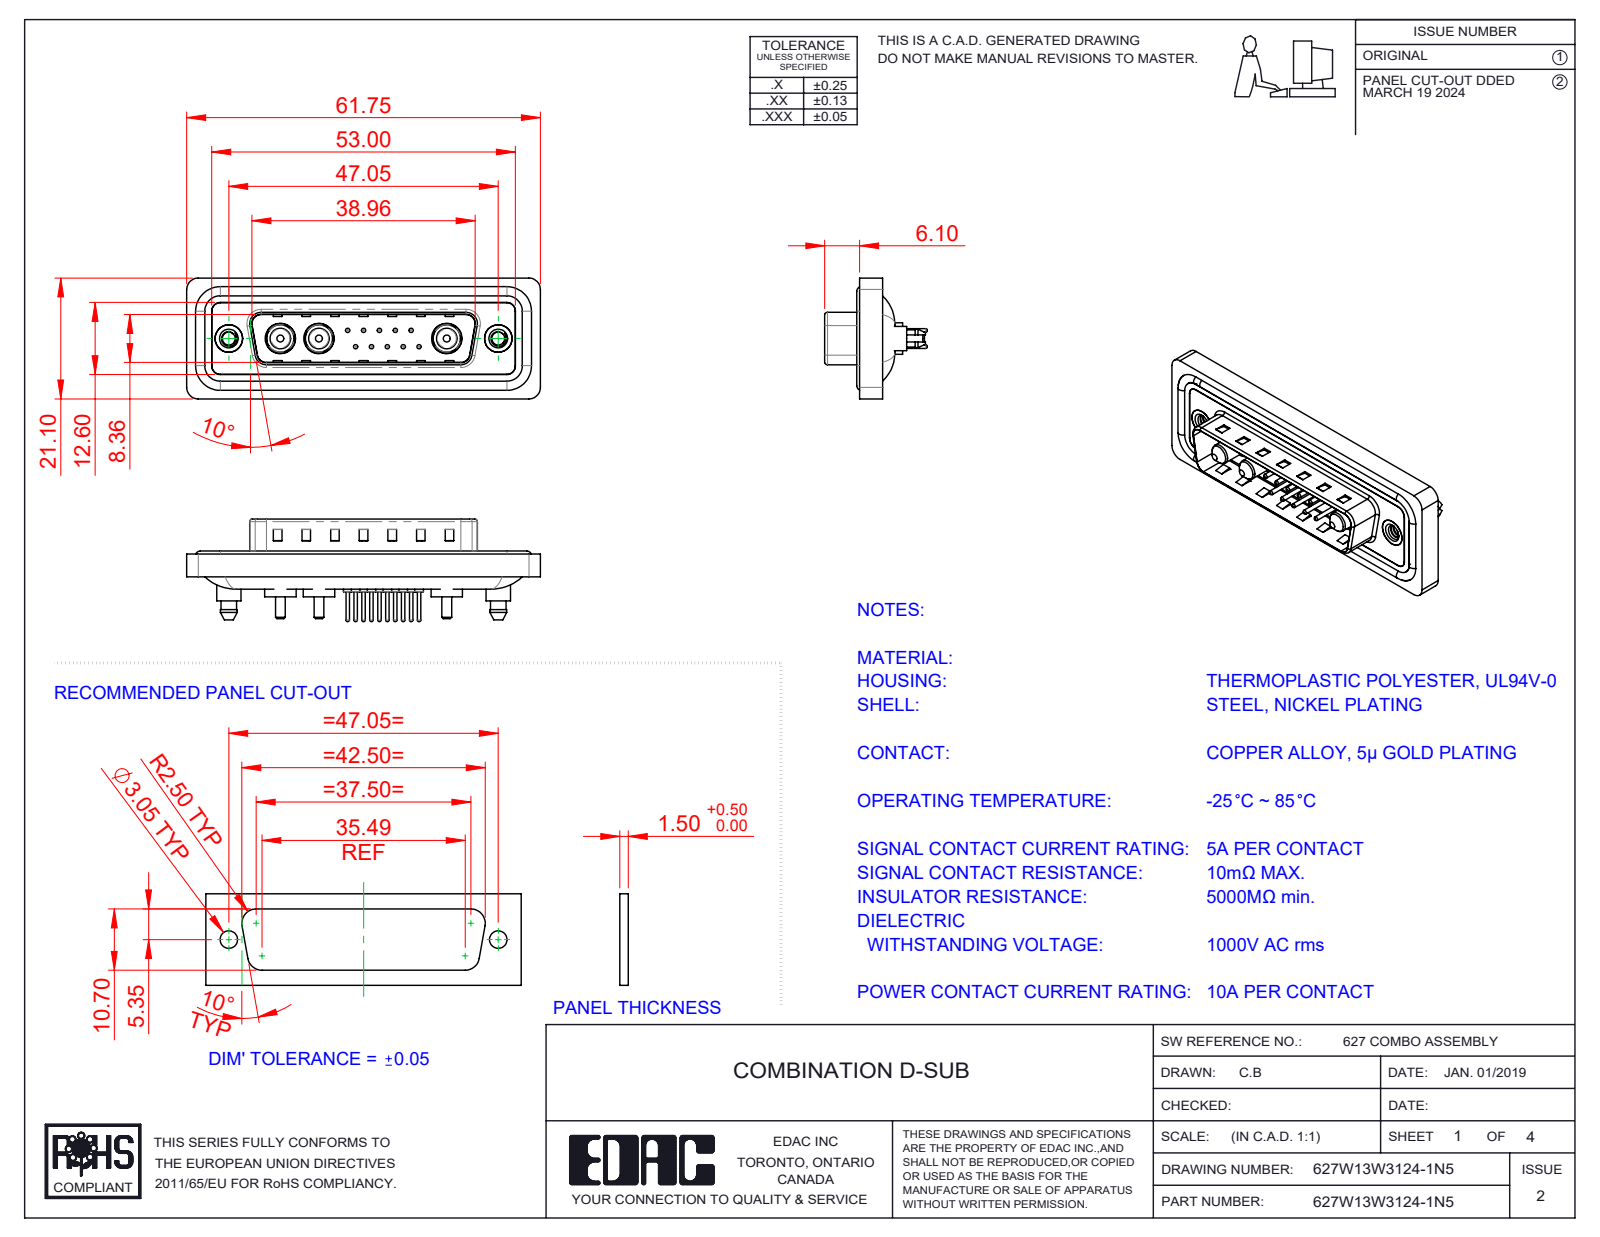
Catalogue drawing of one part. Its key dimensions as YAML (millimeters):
part_name: "627Combo Contact Row 1_24; 627Combo Shell Front_25 Contacts; 627Combo Threaded Boardlock_5; 627Combo Contact Row 2_24 (+5 more)"
step_written_by: "SolidWorks 2023 (CONFIG_CONTROL_DESIGN)"
units: millimeters
bodies: {solids: 23, faces: 1020, planar: 325, cylindrical: 417, other: 278}
overall_size: [61.75, 21.1, 17.9]
volume: 7425
surface_area: 12170
round_holes:
  - {diameter: 0.75, count: 10}
  - {diameter: 1.6, count: 10}
  - {diameter: 2, count: 10}
  - {diameter: 4.85, count: 3}
  - {diameter: 5.3, count: 3}
  - {diameter: 2.26, count: 2}
  - {diameter: 4, count: 2}
  - {diameter: 4.8, count: 2}
  - {diameter: 5, count: 2}
round_bosses_or_shafts:
  - {diameter: 1.5, count: 10}
  - {diameter: 0.6, count: 10}
  - {diameter: 1.6, count: 4}
  - {diameter: 5.5, count: 3}
  - {diameter: 5.2, count: 3}
  - {diameter: 4.75, count: 3}
  - {diameter: 3.75, count: 3}
  - {diameter: 3.6, count: 3}
partial_cylinders:
  - {radius: 1.5, count: 24}
  - {radius: 2, count: 18}
  - {radius: 1.6, count: 10}
  - {radius: 0.5, count: 8}
  - {radius: 0.25, count: 4}
  - {radius: 0.6, count: 4}
  - {radius: 0.65, count: 4}
  - {radius: 0.9, count: 4}
face_to_face_distances: [0.4, 1.5, 1.1, 1.6, 0.5, 3.1, 2.9, 0.82, 9.58, 4.1]
hole_center_spacings: [3.16, 2.77, 5.04, 5.54, 7.49, 5.03, 8.31, 10.11]
